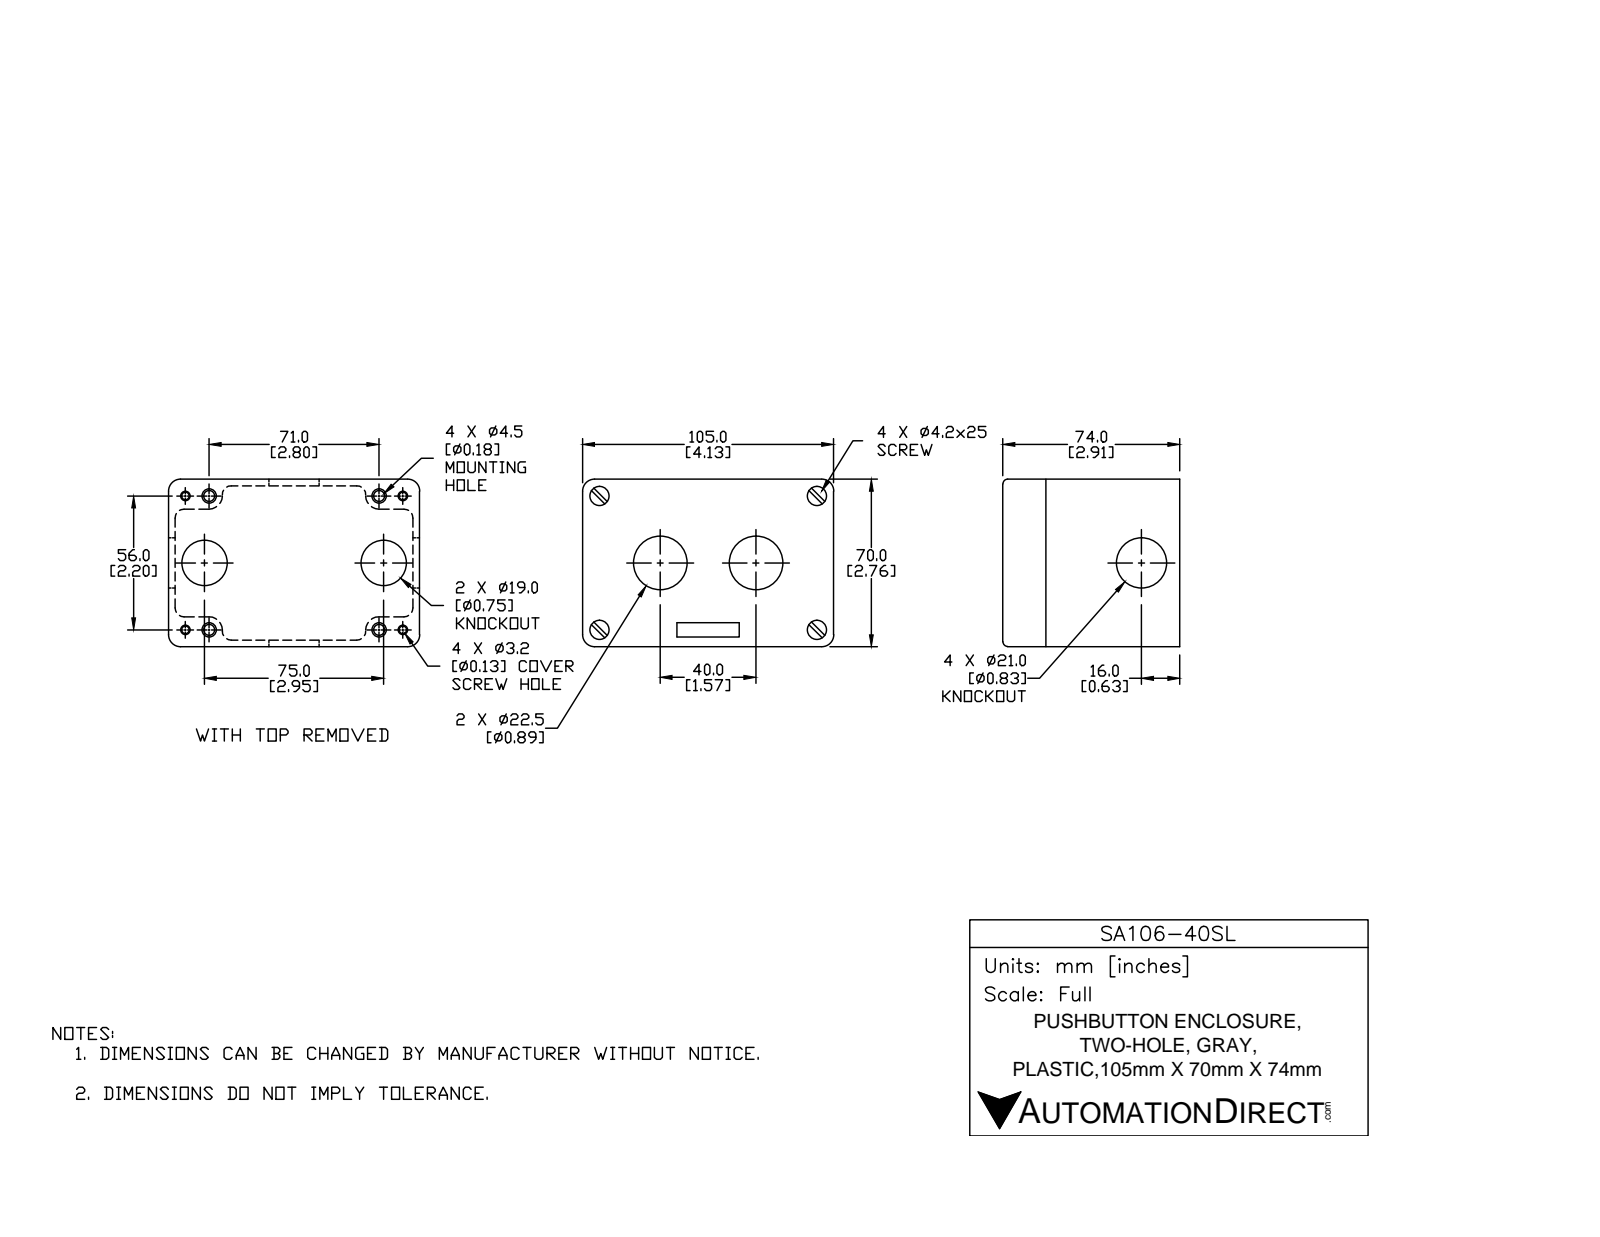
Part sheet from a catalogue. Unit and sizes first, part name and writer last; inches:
Units: inches
Overall size (bounding box): 4.134 × 2.922 × 2.756
Round holes (diameter × count): ⌀0.126 ×4, ⌀0.165 ×4, ⌀0.177 ×4, ⌀0.295 ×4, ⌀0.315 ×4, ⌀0.748 ×2, ⌀0.827 ×2, ⌀0.886 ×2
Round bosses / shafts (diameter × count): ⌀0.291 ×4, ⌀0.11 ×4
Partial cylindrical surfaces — rounded edges, fillets, slot ends (radius × count): R0.02 ×16, R0.041 ×8, R0.095 ×8, R0.039 ×4, R0.071 ×4, R0.197 ×4, R0.259 ×4, R0.323 ×4
Main face-to-face distances: 0.102, 2.756, 2.915, 2.654, 0.087, 2.829, 4.032, 4.134, 0.079, 2.837
Hole centre spacings: 0.394, 1.105, 1.146, 1.26, 1.491, 2.205, 2.24, 2.447
Volume: 9.241 in³ · Surface area: 129.2 in²
Bodies: 6 solids, 470 faces (126 planar, 192 cylindrical, 152 other)
Part name (STEP PRODUCT): SA106-40SL
STEP written by: SolidWorks 2018 (AUTOMOTIVE_DESIGN)
